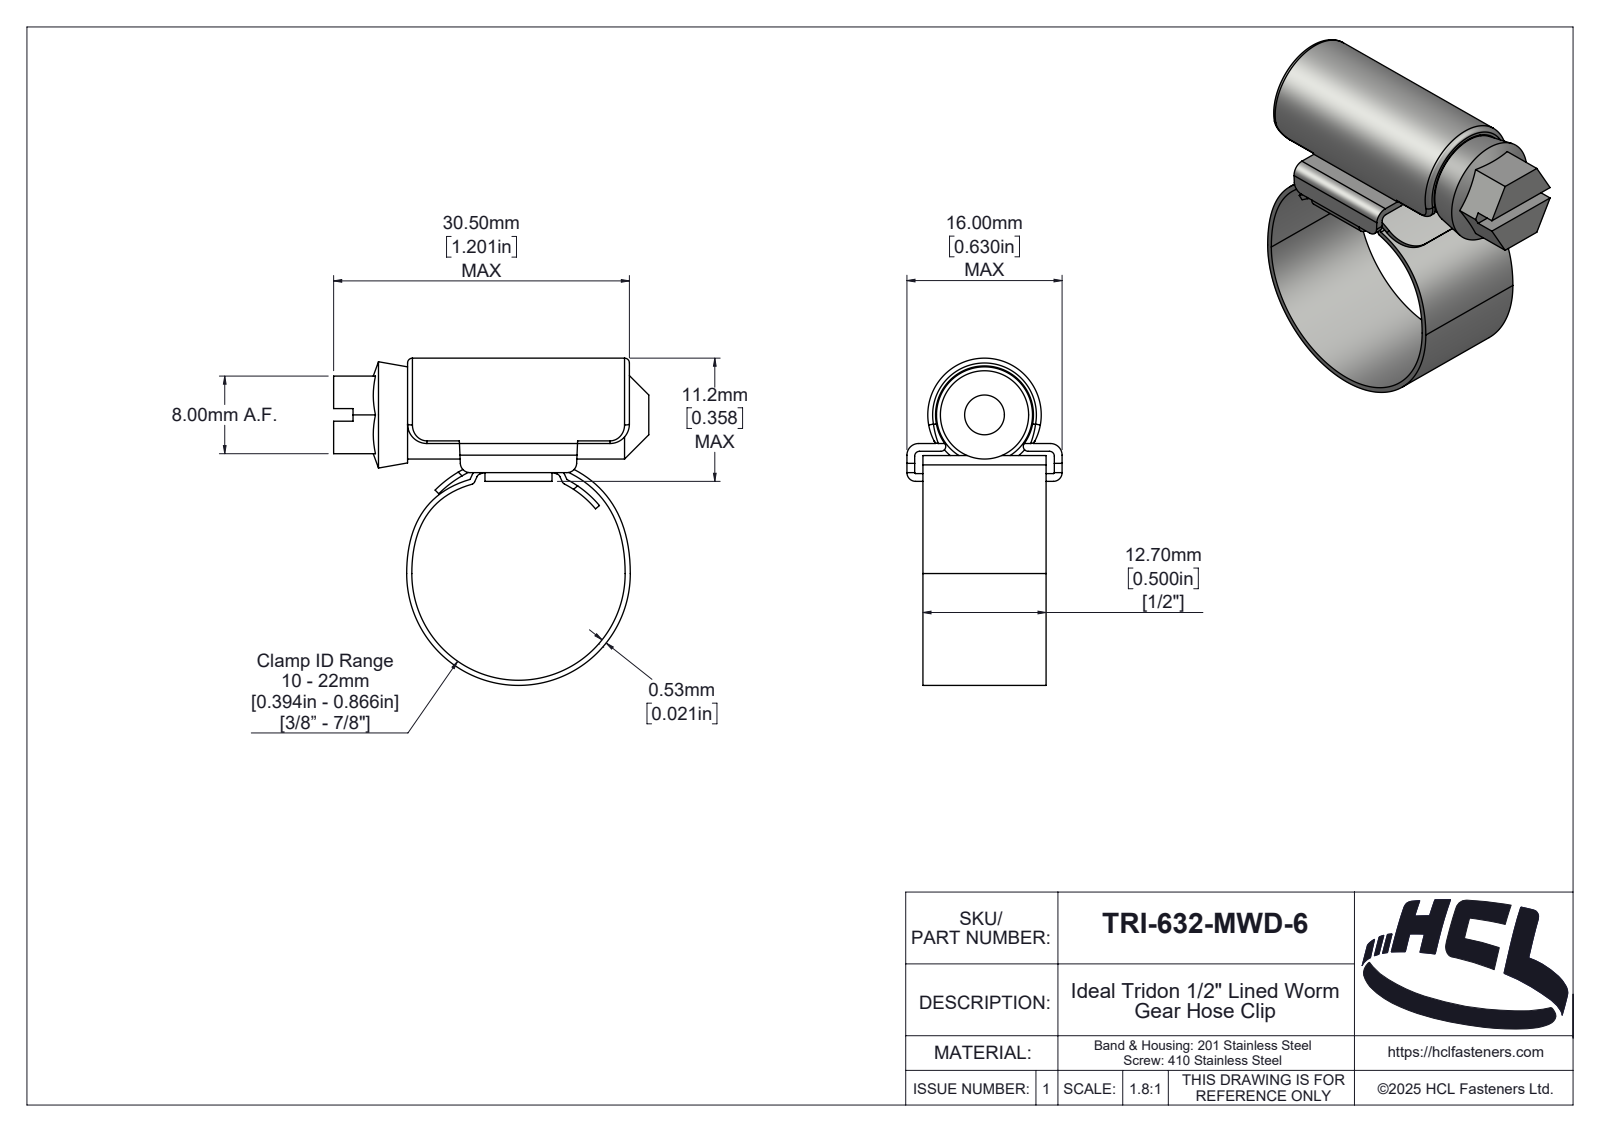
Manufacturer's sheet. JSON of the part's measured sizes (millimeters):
{"part_name": "TRI-632-MWD-6", "step_written_by": "SolidWorks 2025 (AUTOMOTIVE_DESIGN)", "units": "millimeters", "bodies": {"solids": 3, "faces": 217, "planar": 49, "cylindrical": 99, "other": 69}, "overall_size": [33.73, 32.5, 16], "volume_mm3": 3269, "surface_area_mm2": 5129, "round_bosses_or_shafts": [[9.1, 1]], "partial_cylinders_radius": [[0.5, 10], [3, 4], [0.1, 2], [0.9, 2], [1, 2], [1.03, 2], [1.2, 2], [2, 2]], "face_to_face_distances": [0.8, 3.1, 2.3, 3.9, 12.7, 1.65, 14.35, 15.2, 0.85, 13.55]}
